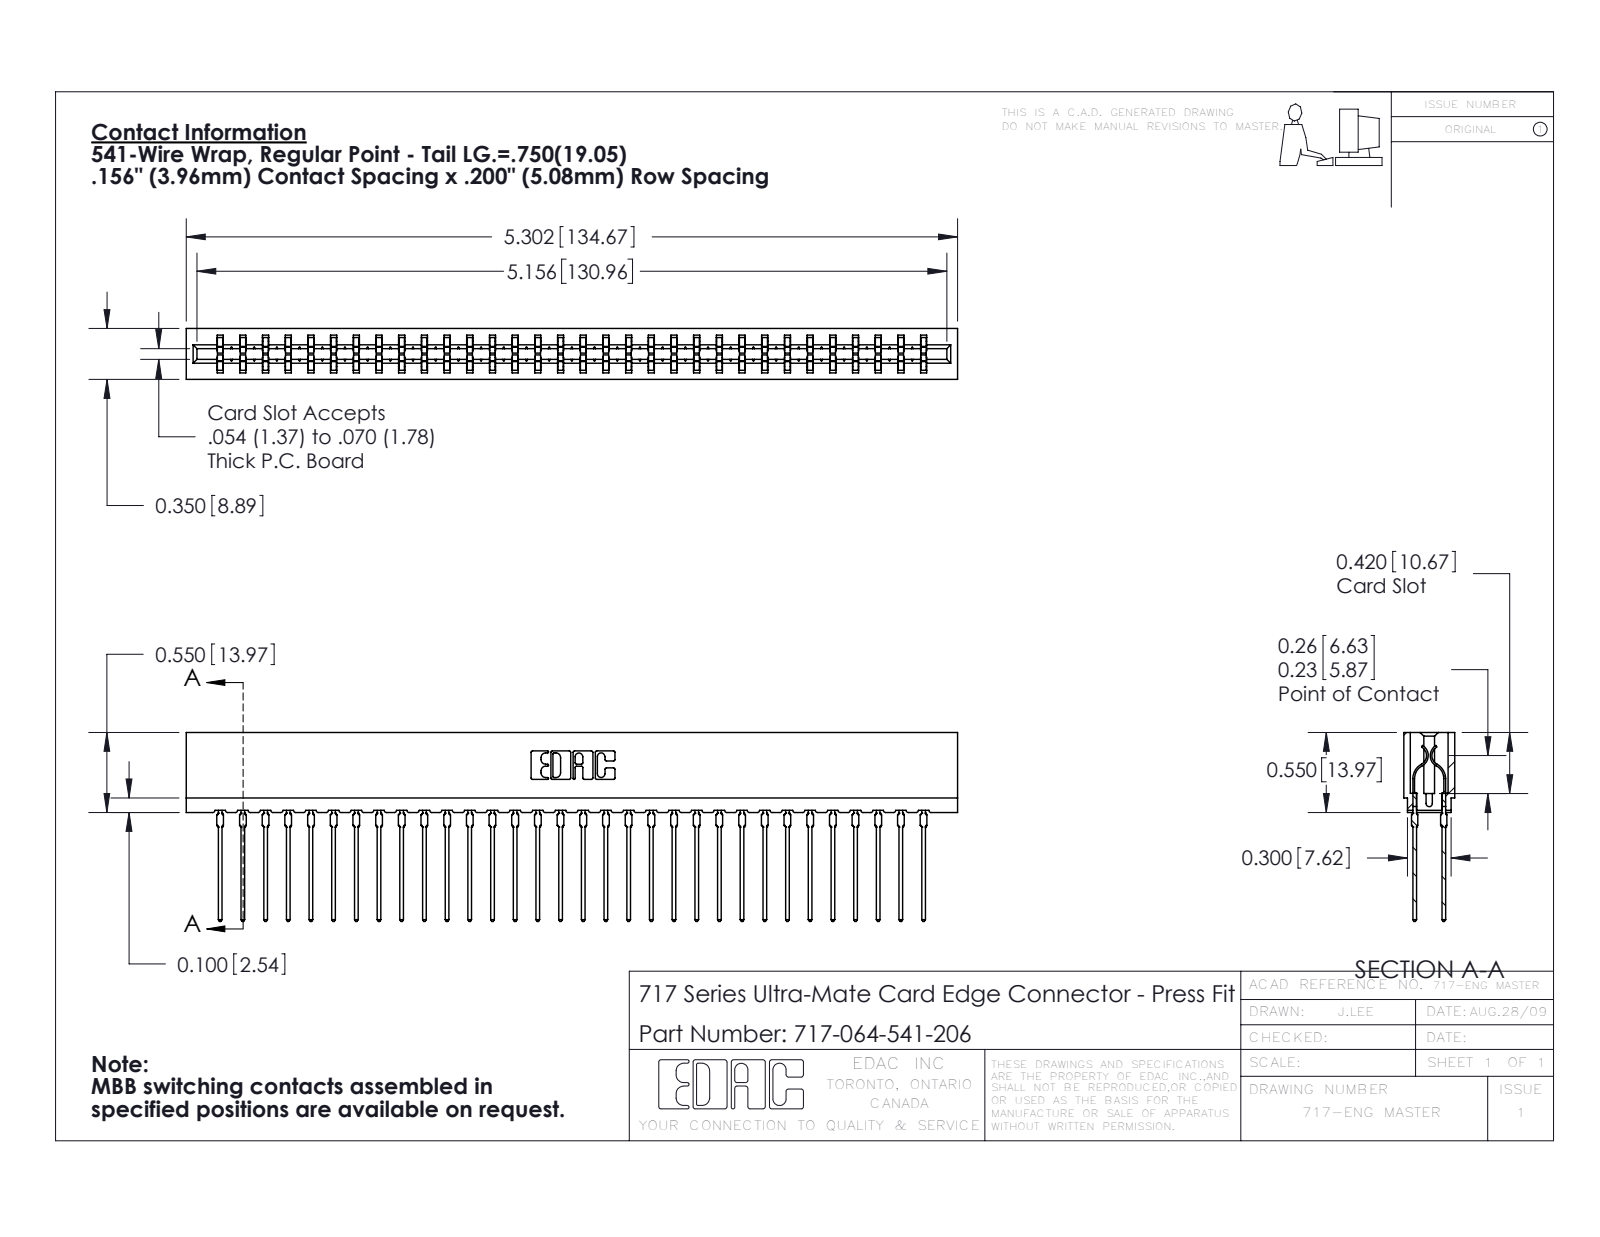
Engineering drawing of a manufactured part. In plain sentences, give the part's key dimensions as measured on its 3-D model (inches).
The part is named "745-292-001_541; 717 Part_Insulator Option - 06; 717-064-541-206". Its 3-D file was written by "SolidWorks 2016 (CONFIG_CONTROL_DESIGN)". It is 65 solids with 5854 faces: 3030 planar, 1160 cylindrical and 1664 other. Overall it measures 5.302 by 1.299 by 0.35 inches. Its volume is 0.734 cubic inches and its surface area 30.51 square inches. Partial cylindrical surfaces (rounded edges, fillets, slot ends): 128 of radius 0.021, 64 of radius 0.015, 22 of radius 0.01, 8 of radius 0.005, 8 of radius 0.011, 6 of radius 0.007, 6 of radius 0.031, 3 of radius 0.026. The main face-to-face distances are 0.212, 0.138, 0.35, 0.063, 0.287, 0.076, 0.149, 0.087, 0.263, 0.025.
